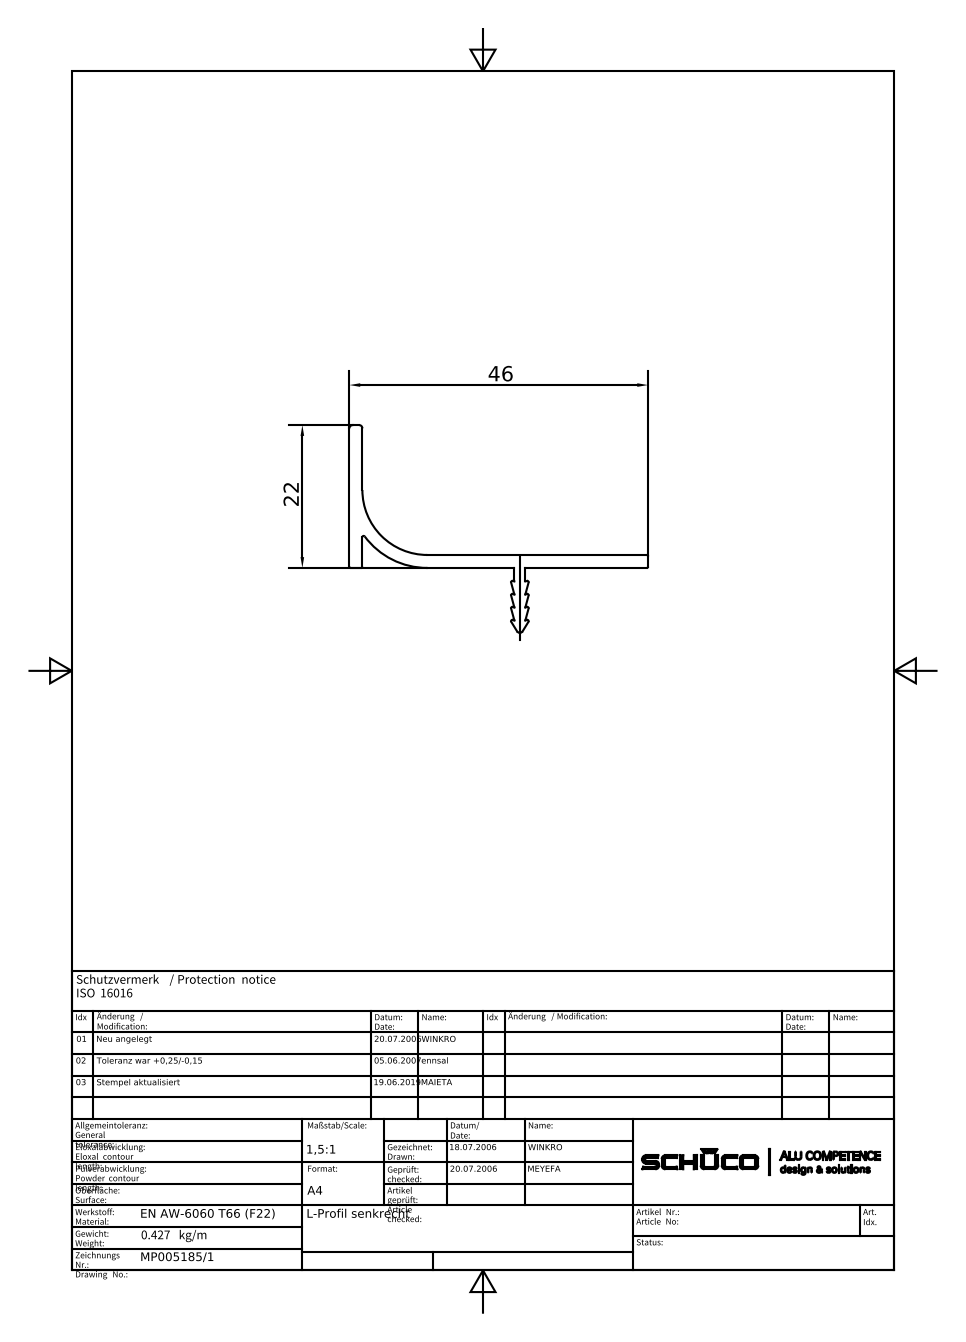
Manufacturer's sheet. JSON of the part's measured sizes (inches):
{"part_name": "MP00518501", "step_written_by": "Autodesk Inventor 2015 (AUTOMOTIVE_DESIGN)", "units": "inches", "bodies": {"solids": 1, "faces": 47, "planar": 29, "cylindrical": 18, "other": 0}, "overall_size": [1.811, 1.26, 0.394], "volume_in3": 0.096, "surface_area_in2": 2.987, "partial_cylinders_radius": [[0.008, 13], [0.02, 3], [0.394, 1], [0.472, 1]], "face_to_face_distances": [0.079, 0.394, 0.02, 0.921, 1, 0.067, 0.988, 1.067, 0.021, 0.041]}
